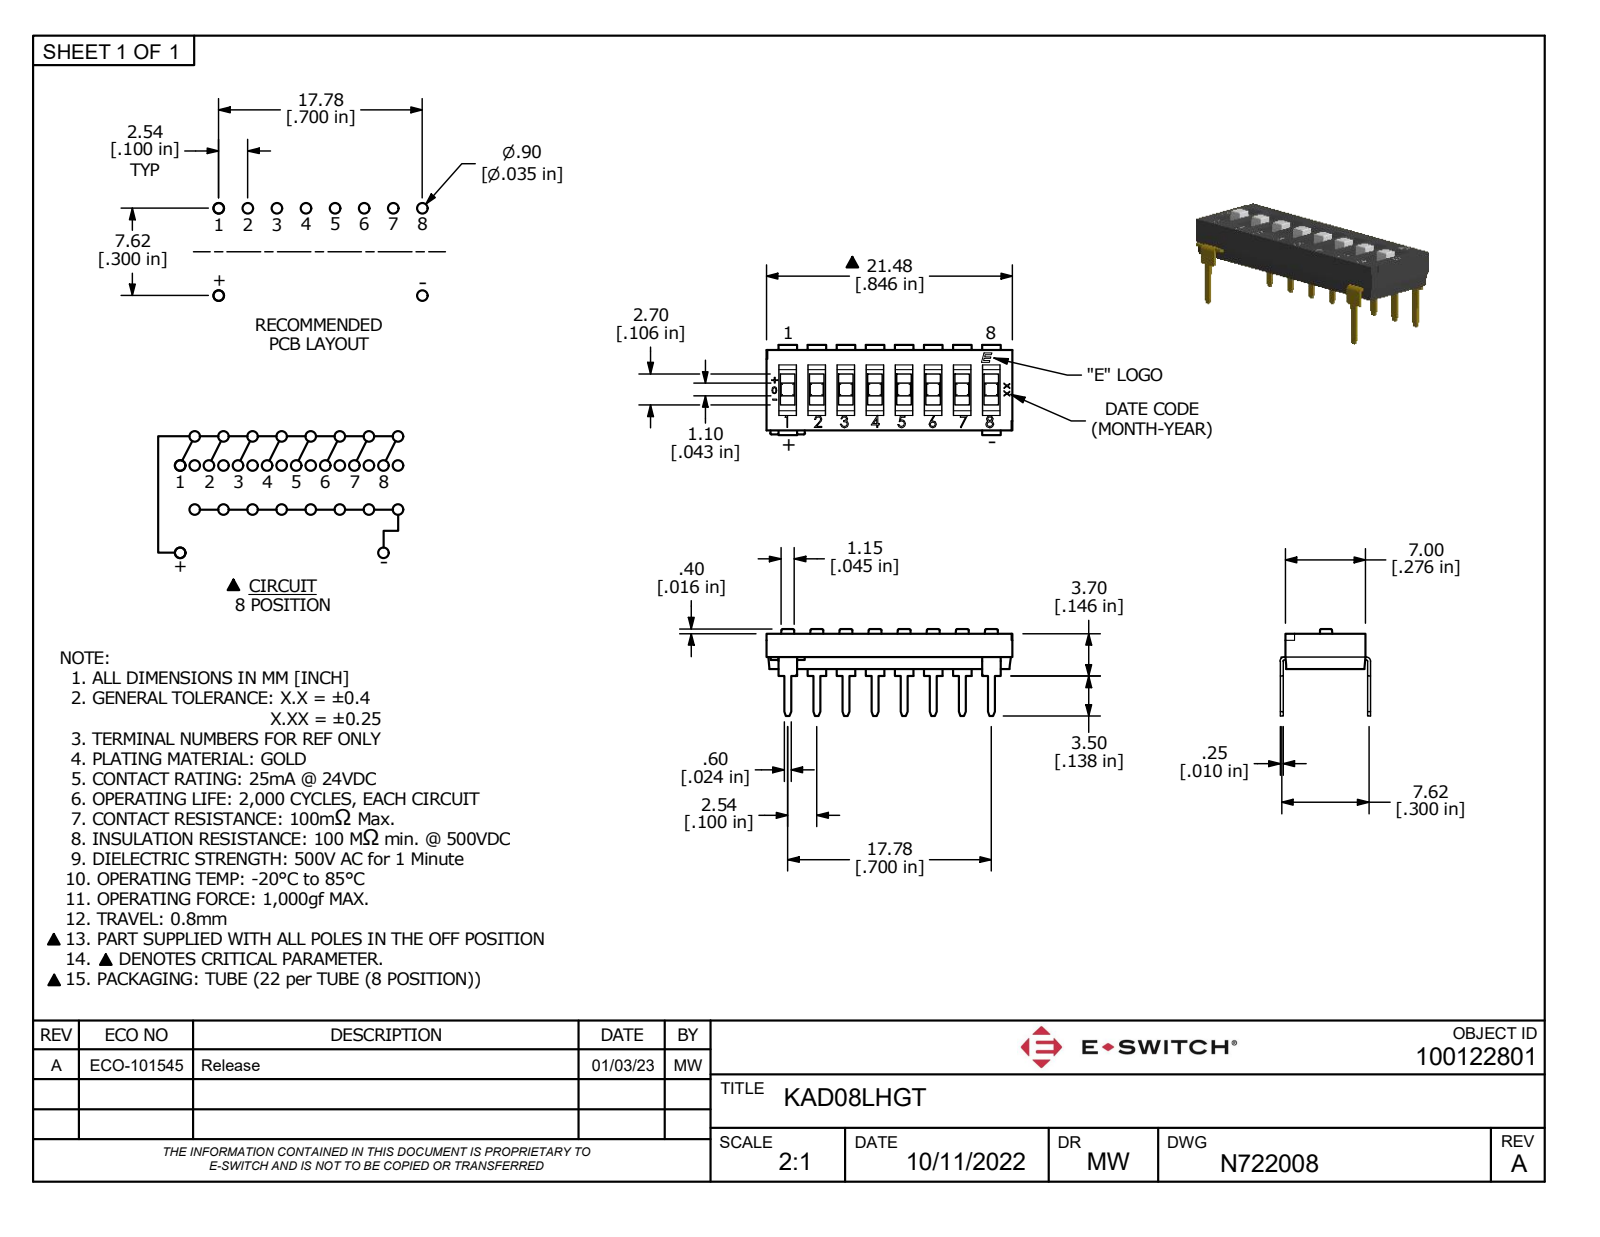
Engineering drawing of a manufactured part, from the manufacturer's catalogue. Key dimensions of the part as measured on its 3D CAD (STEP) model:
Part name (STEP PRODUCT): KAD08LHGT
STEP written by: Autodesk Inventor 2022 (AUTOMOTIVE_DESIGN)
Units: millimetres
Bodies: 1 solid, 555 faces (428 planar, 56 cylindrical, 71 other)
Overall size (bounding box): 21.48 × 7.87 × 7.6
Volume: 455 mm³ · Surface area: 690 mm²
Partial cylindrical surfaces — rounded edges, fillets, slot ends (radius × count): R0.1 ×24, R0.15 ×2, R0.35 ×2
Main face-to-face distances: 3.1, 7, 0.44, 7.19, 7.62, 7.44, 2.54, 5.08, 2.69, 0.41
